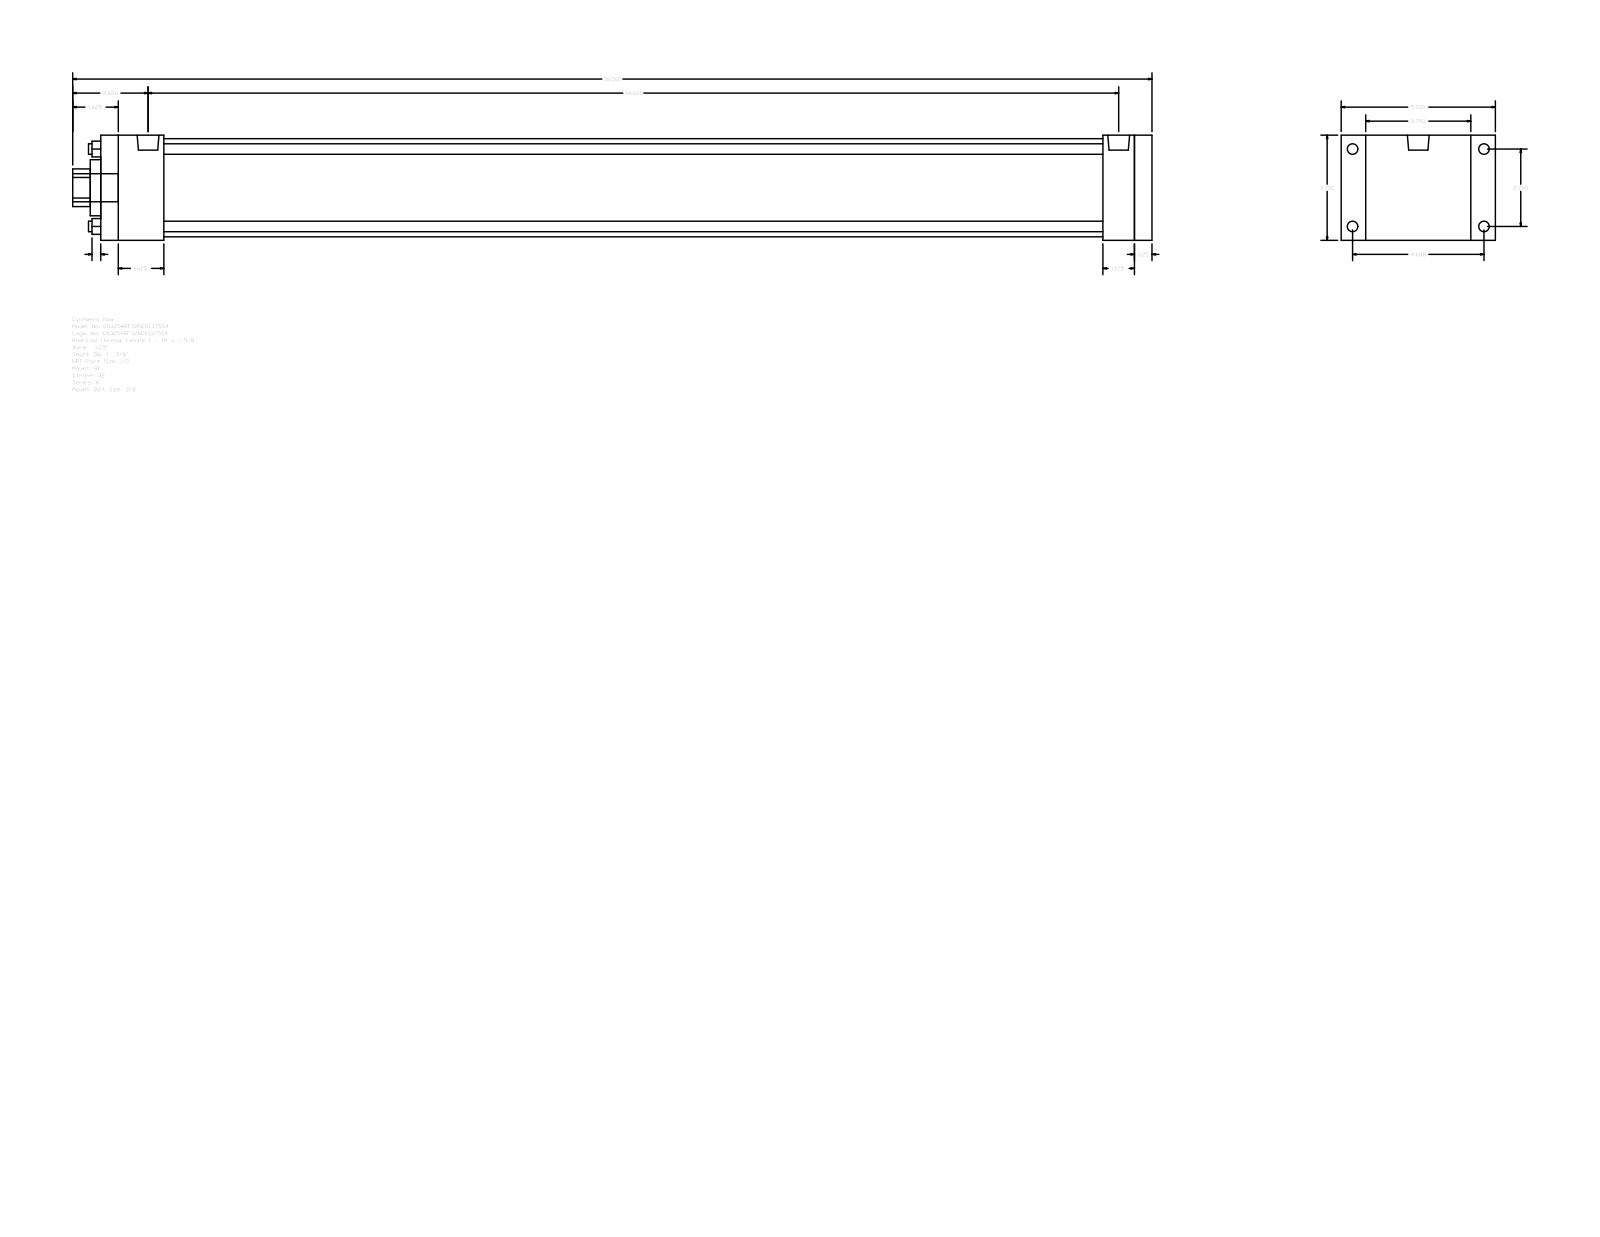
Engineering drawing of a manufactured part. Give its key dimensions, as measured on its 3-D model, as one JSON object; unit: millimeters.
{"part_name": "A_RF__0325_1.375", "step_written_by": "GSSL Pune (CONFIG_CONTROL_DESIGN)", "units": "millimeters", "bodies": {"solids": 0, "faces": 92, "planar": 64, "cylindrical": 28, "other": 0}, "overall_size": [977.9, 139.7, 95.25], "round_holes": [[9.53, 4], [34.92, 1], [50.8, 1], [88.9, 1]], "round_bosses_or_shafts": [[9.53, 4], [8.73, 4], [19.77, 2], [25.4, 1]], "partial_cylinders_radius": [[17.06, 1]], "face_to_face_distances": [95.24, 952.5, 15.88, 936.62, 22.23, 117.47, 28.57, 908.05, 44.45, 57.15], "hole_center_spacings": [49.57, 70.1, 99.14]}
